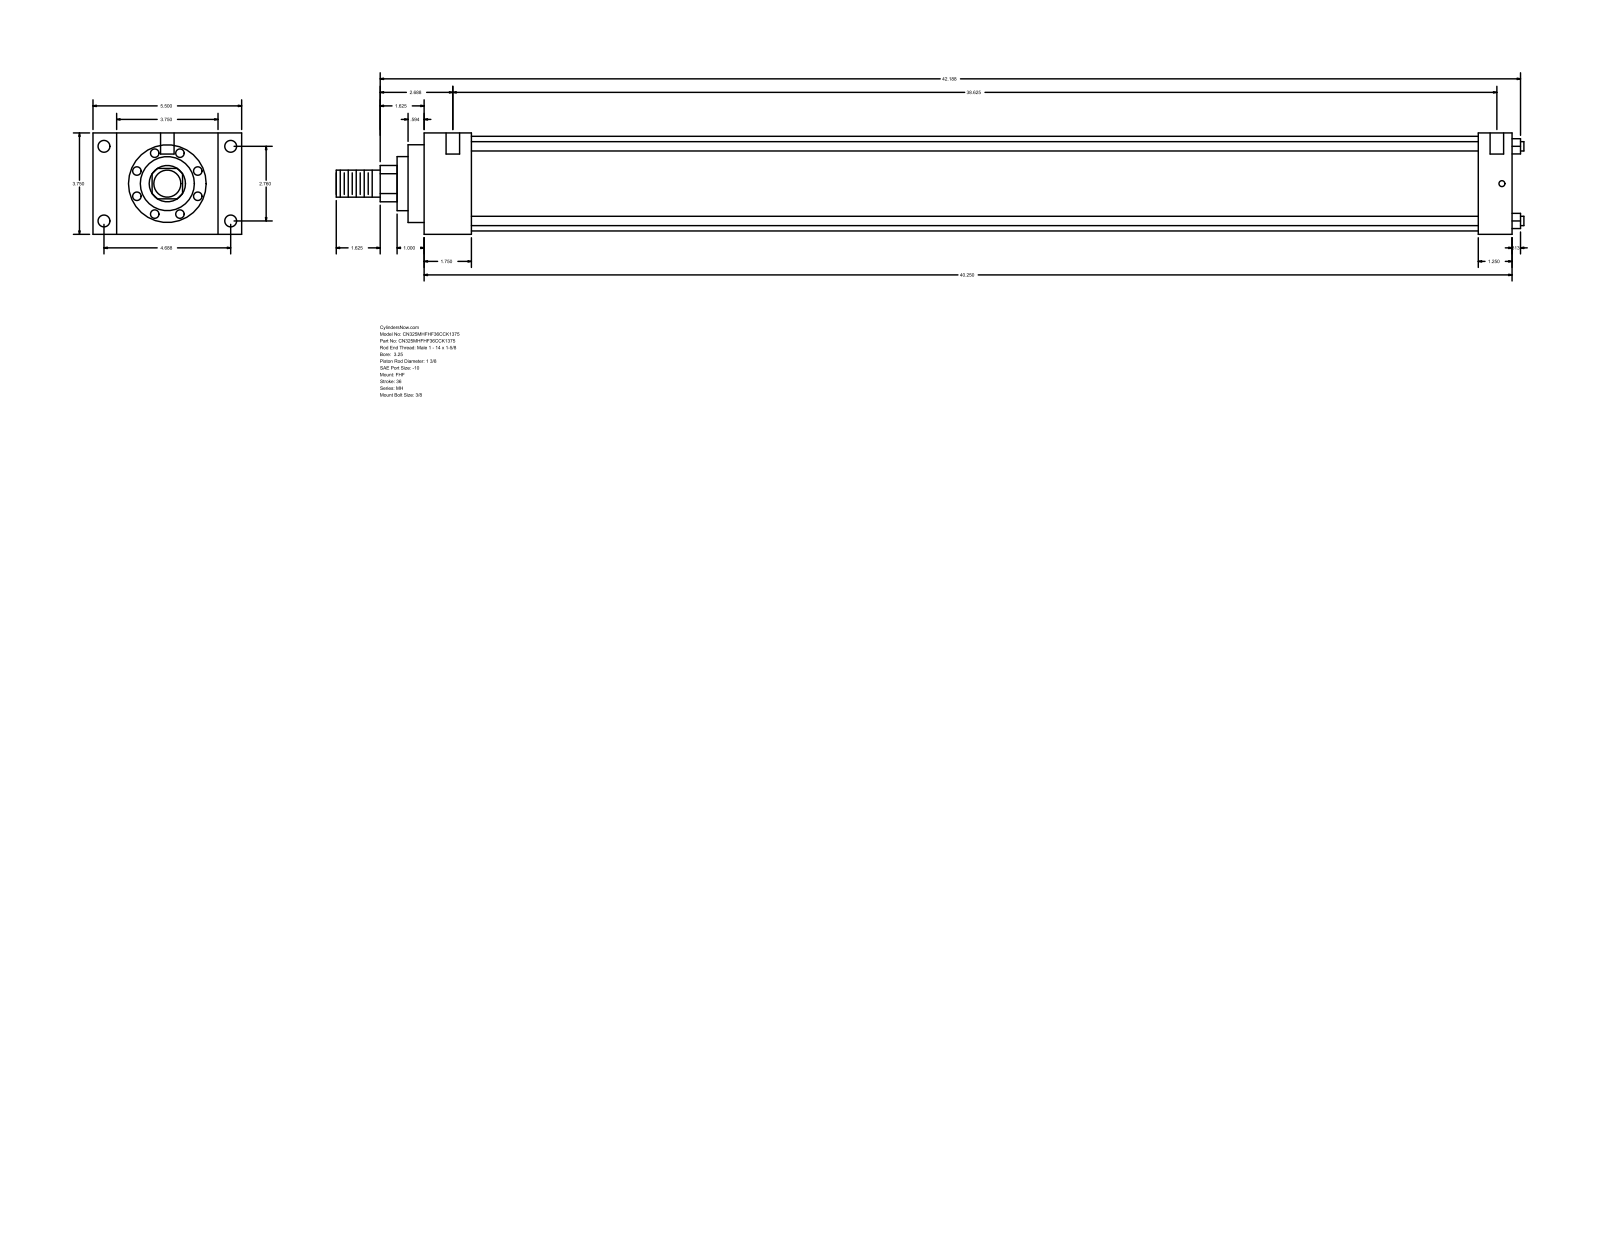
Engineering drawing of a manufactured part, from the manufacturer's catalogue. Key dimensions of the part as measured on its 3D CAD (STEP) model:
Part name (STEP PRODUCT): MH_FHF__0325_1.375
STEP written by: GSSL Pune (CONFIG_CONTROL_DESIGN)
Units: millimetres
Bodies: 0 solids, 90 faces (61 planar, 29 cylindrical, 0 other)
Overall size (bounding box): 1116.01 × 139.7 × 95.25
Round holes (diameter × count): ⌀5.56 ×4, ⌀11.13 ×4, ⌀12.7 ×2
Round bosses / shafts (diameter × count): ⌀8.76 ×4, ⌀88.9 ×1, ⌀73.03 ×1, ⌀50.8 ×1, ⌀34.92 ×1, ⌀25.4 ×1
Partial cylindrical surfaces — rounded edges, fillets, slot ends (radius × count): R17.06 ×1
Main face-to-face distances: 95.24, 1022.35, 44.45, 977.9, 22.23, 117.47, 139.7, 990.61, 946.16, 31.74
Hole centre spacings: 70.1, 119.06, 138.16, 987.43, 1.59, 4.76, 981.08, 982.67
